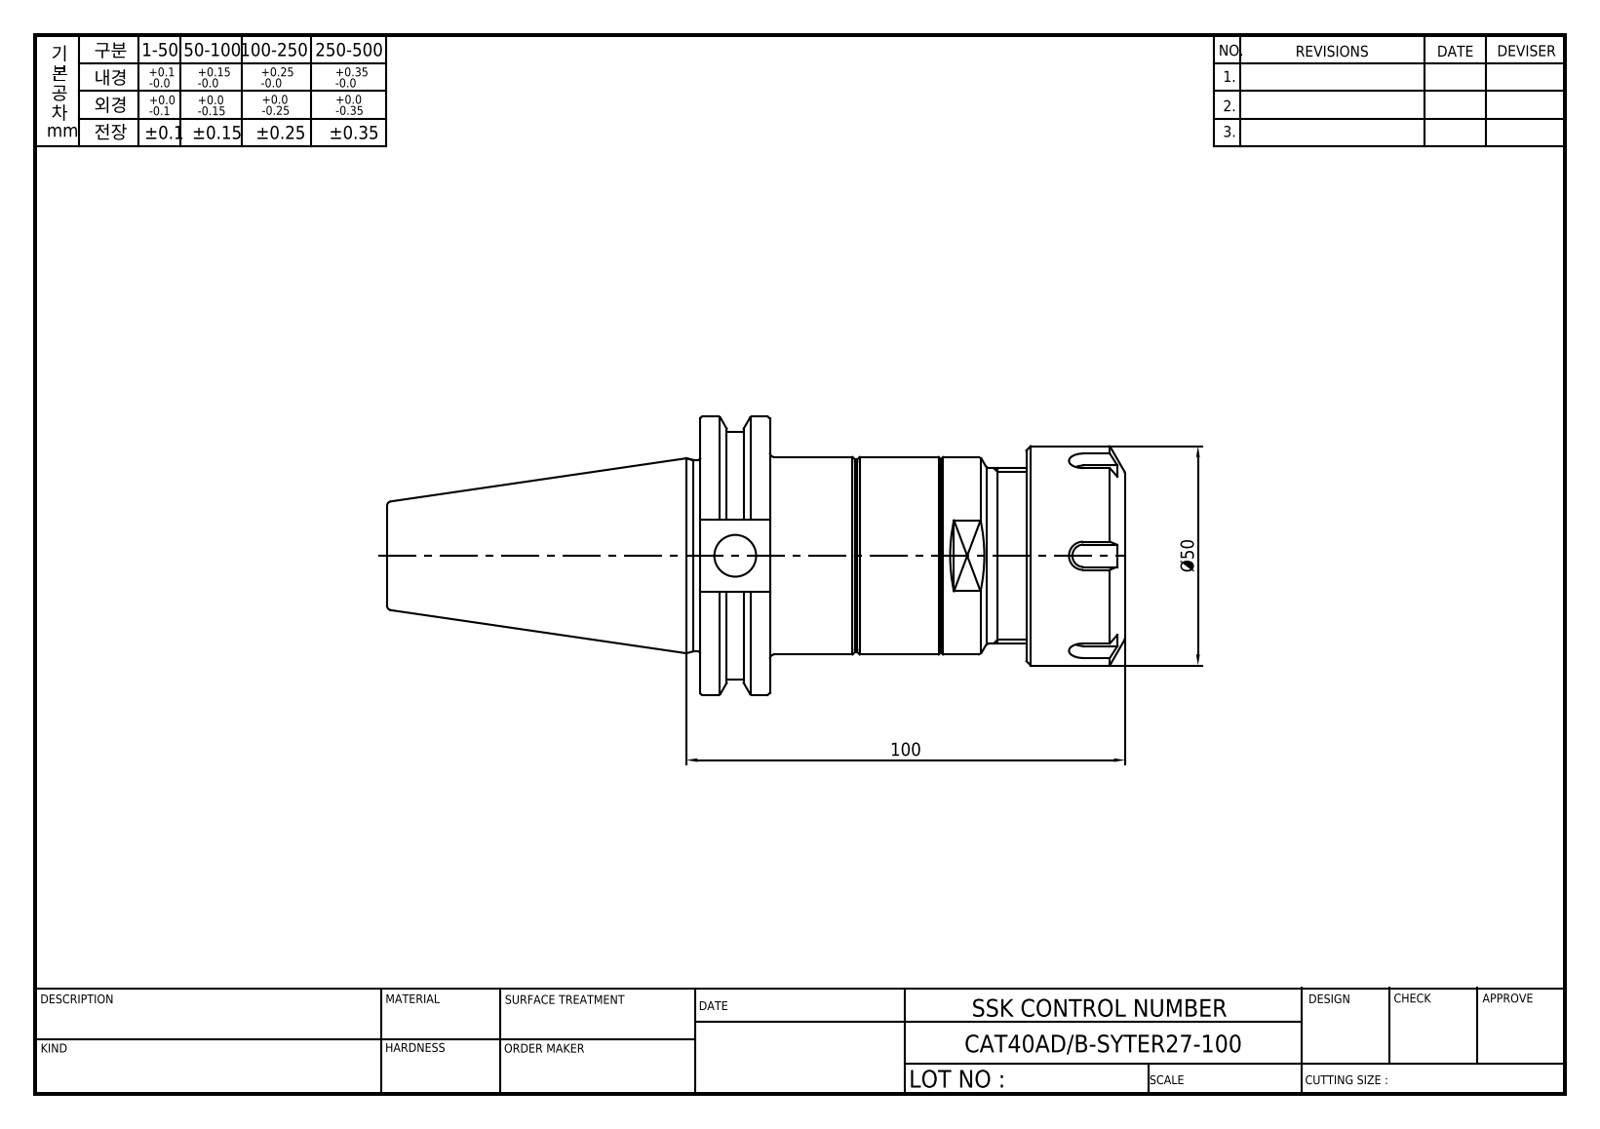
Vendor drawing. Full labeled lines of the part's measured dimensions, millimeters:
Part name (STEP PRODUCT): LO-CAT40ADB-SYTER27-100; SYTER27-COVER(BLUE); SYNCHRO-ER32-42; ER32NUT
STEP written by: Autodesk Inventor 2025 (AUTOMOTIVE_DESIGN)
Units: millimetres
Bodies: 4 solids, 253 faces (98 planar, 74 cylindrical, 81 other)
Overall size (bounding box): 168.25 × 63.5 × 61.09
Volume: 193 435 mm³ · Surface area: 54 569 mm²
Round holes (diameter × count): ⌀3.24 ×4, ⌀5 ×4, ⌀5.1 ×4, ⌀4 ×2, ⌀4.2 ×2, ⌀1 ×1, ⌀4.92 ×1, ⌀6.2 ×1, ⌀6.5 ×1, ⌀9.53 ×1, ⌀13.39 ×1, ⌀15 ×1
Round bosses / shafts (diameter × count): ⌀63.5 ×1, ⌀50 ×1, ⌀45 ×1, ⌀43.6 ×1, ⌀41 ×1, ⌀40 ×1, ⌀38.4 ×1, ⌀33.7 ×1
Partial cylindrical surfaces — rounded edges, fillets, slot ends (radius × count): R0.5 ×12, R28.15 ×1
Main face-to-face distances: 15.88, 0.4, 22.5, 40.13, 24.25, 7.9, 39.73, 23.85, 12.5, 96.83
Hole centre spacings: 12.5, 17.68, 25, 0.33, 17.45, 17.91, 11.7, 12.53
